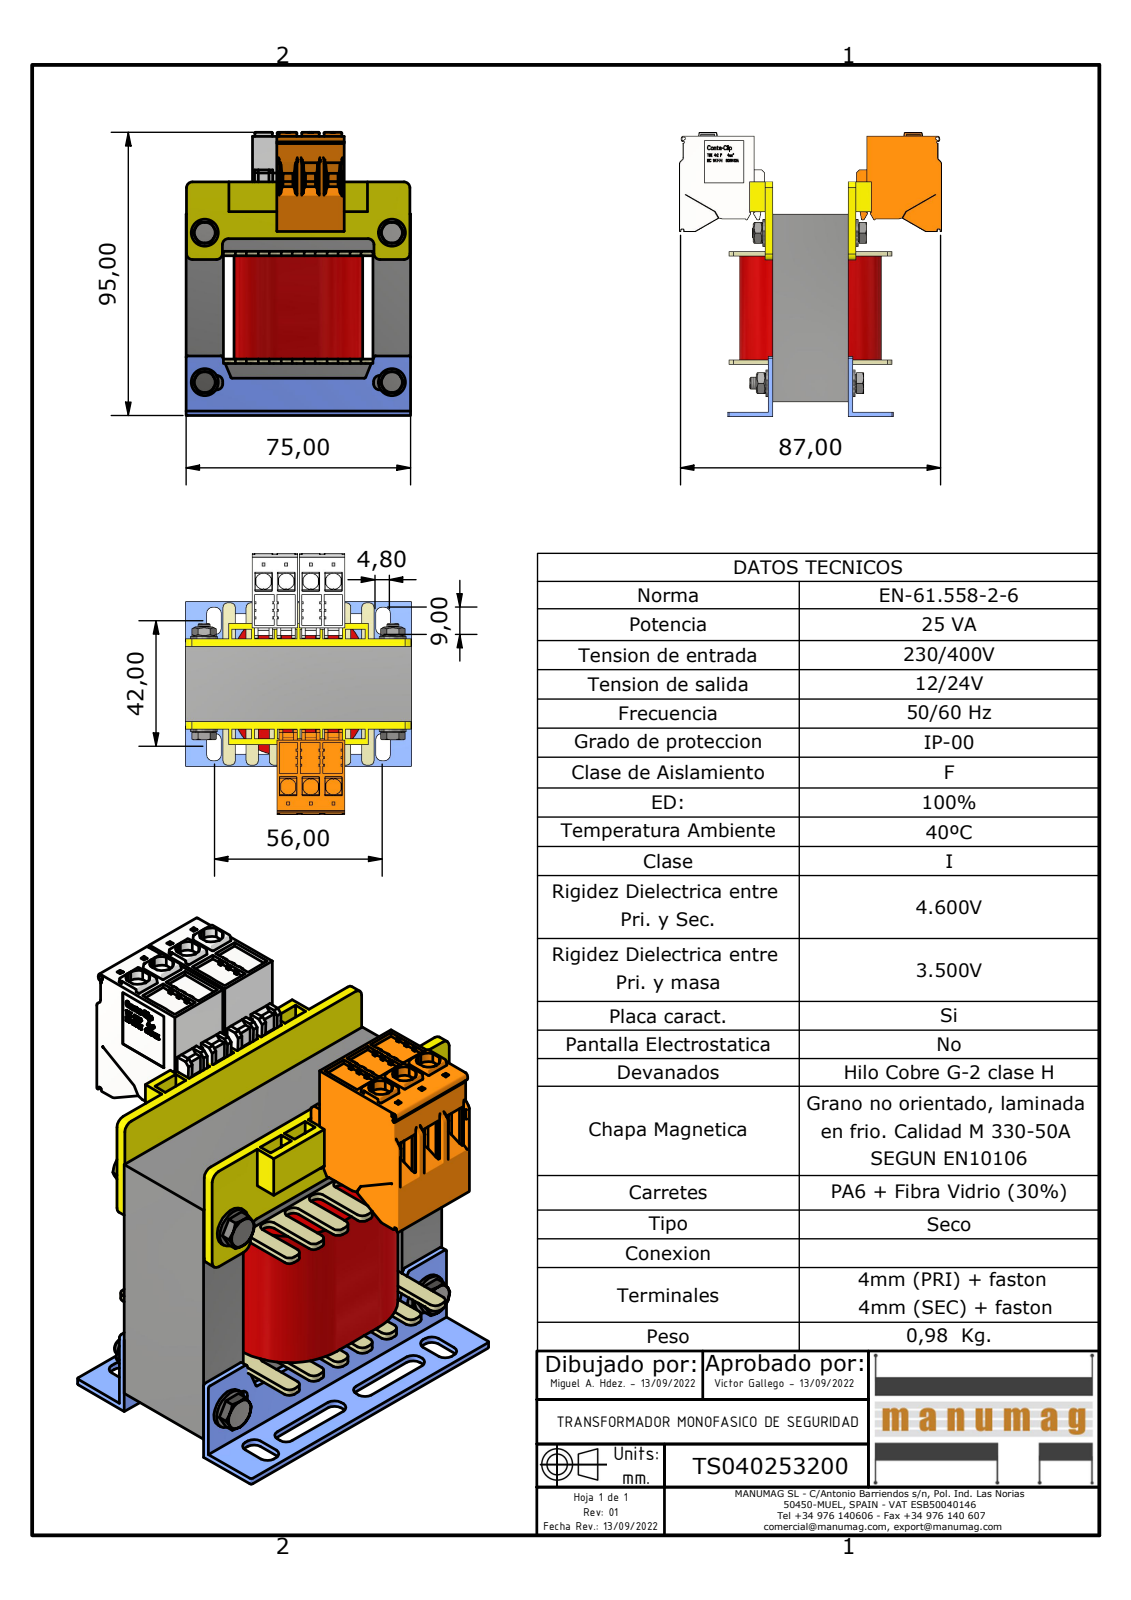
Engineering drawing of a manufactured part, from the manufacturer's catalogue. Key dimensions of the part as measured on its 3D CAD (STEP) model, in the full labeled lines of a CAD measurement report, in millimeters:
Part name (STEP PRODUCT): TS040253200; EI75 x 62,5 - 25 (RC25); AF25DIN; EI75 (+6 more)
STEP written by: Autodesk Inventor 2023 (AUTOMOTIVE_DESIGN)
Units: millimetres
Bodies: 25 solids, 5918 faces (4734 planar, 821 cylindrical, 363 other)
Overall size (bounding box): 94.6 × 86.9 × 75
Volume: 185 000 mm³ · Surface area: 80 060 mm²
Round holes (diameter × count): ⌀3.3 ×4, ⌀4.3 ×4, ⌀4.5 ×4, ⌀4 ×2
Round bosses / shafts (diameter × count): ⌀9 ×4, ⌀5.9 ×4, ⌀3.6 ×4, ⌀4 ×2
Partial cylindrical surfaces — rounded edges, fillets, slot ends (radius × count): R0.2 ×259, R0.2 ×81, R1.5 ×52, R2 ×48, R0.5 ×32, R0.3 ×12, R1 ×8, R2.7 ×7
Main face-to-face distances: 25, 12.5, 50, 1.5, 37.5, 62.5, 2.5, 27.5, 36, 17.4
Hole centre spacings: 50, 62.5, 80
